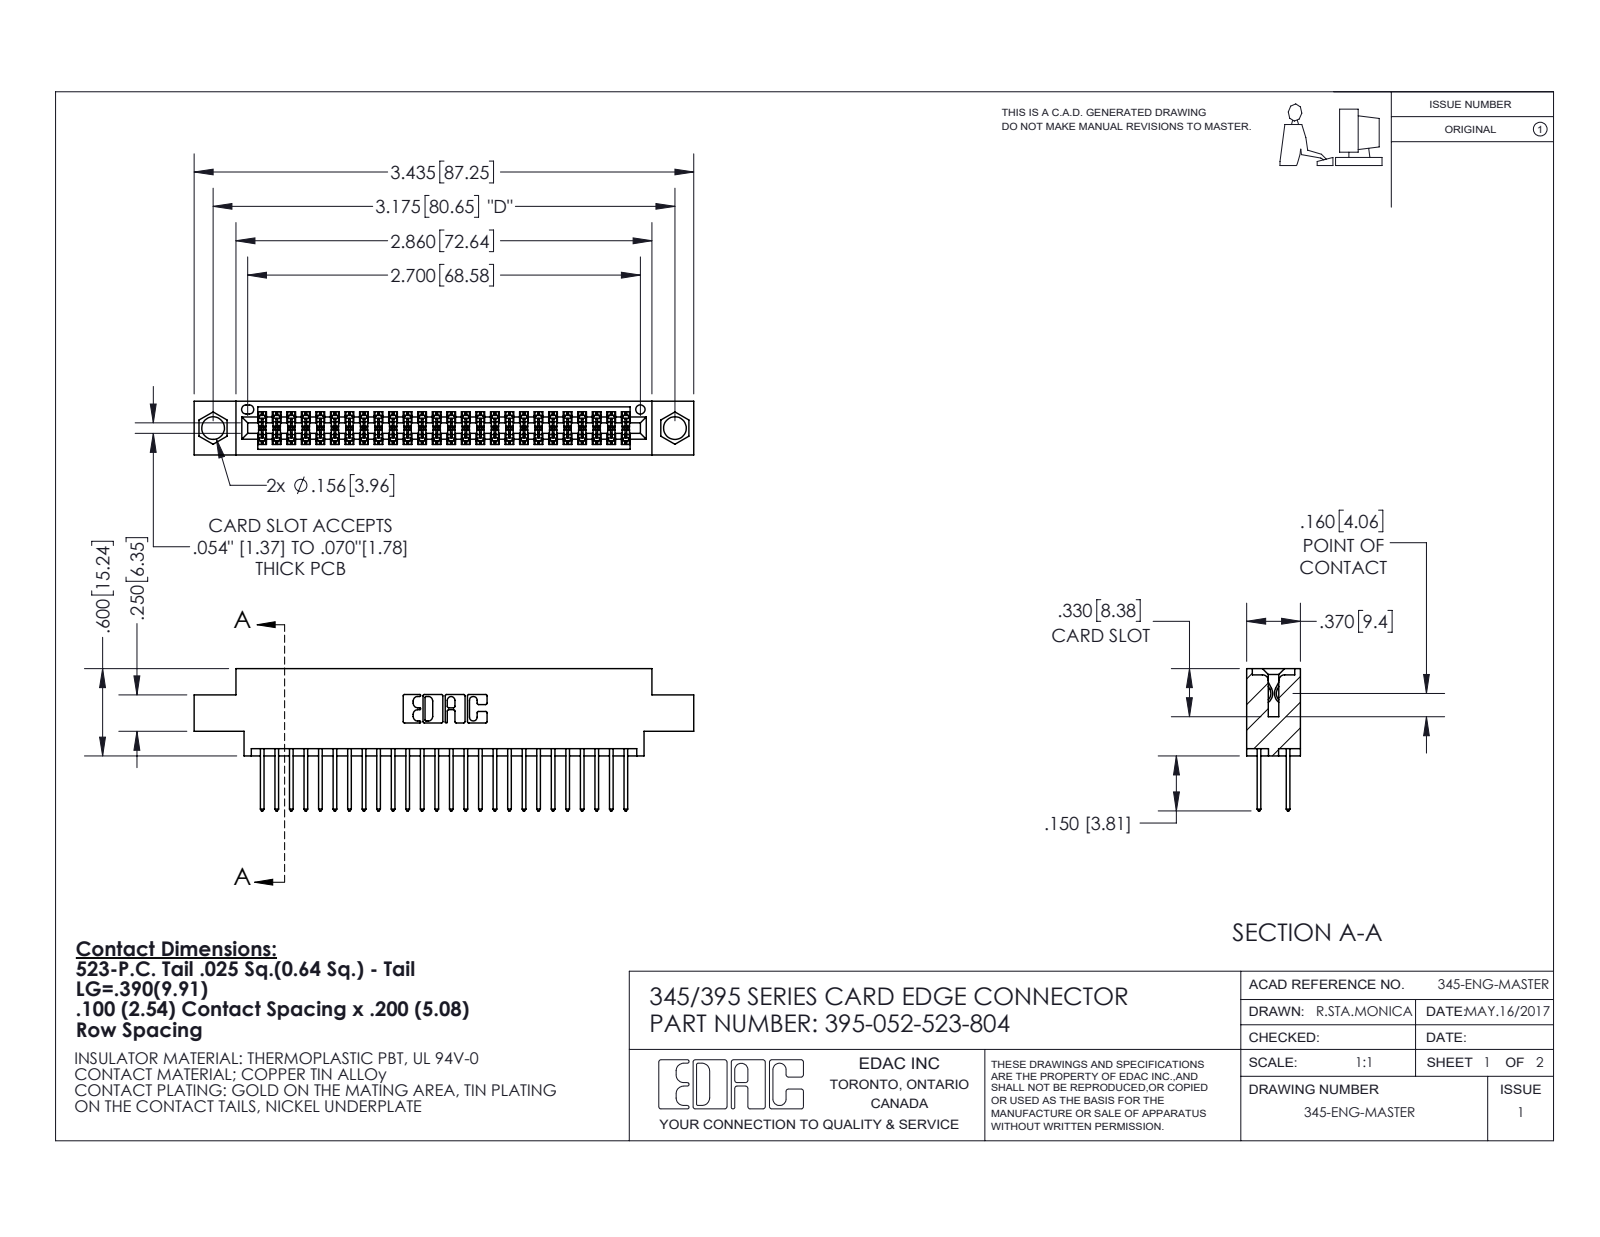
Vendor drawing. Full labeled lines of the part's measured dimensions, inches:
Part name (STEP PRODUCT): 345-292-001_345-293-123; 345 Part_0.170 Offset - 0.156 Dia-TI; 395-052-523-804
STEP written by: SolidWorks 2020 (CONFIG_CONTROL_DESIGN)
Units: inches
Bodies: 53 solids, 2744 faces (1814 planar, 930 cylindrical, 0 other)
Overall size (bounding box): 3.435 × 0.977 × 0.37
Volume: 0.501 in³ · Surface area: 19.07 in²
Round holes (diameter × count): ⌀0.156 ×2, ⌀0.064 ×1
Partial cylindrical surfaces — rounded edges, fillets, slot ends (radius × count): R0.006 ×78, R0.01 ×52, R0.01 ×22, R0.007 ×6, R0.031 ×6, R0.026 ×3, R0.014 ×2, R0.019 ×2
Main face-to-face distances: 0.072, 0.298, 0.2, 0.098, 0.272, 0.025, 0.37, 0.225, 0.175, 0.149
Hole centre spacings: 0.27, 2.94, 3.175
